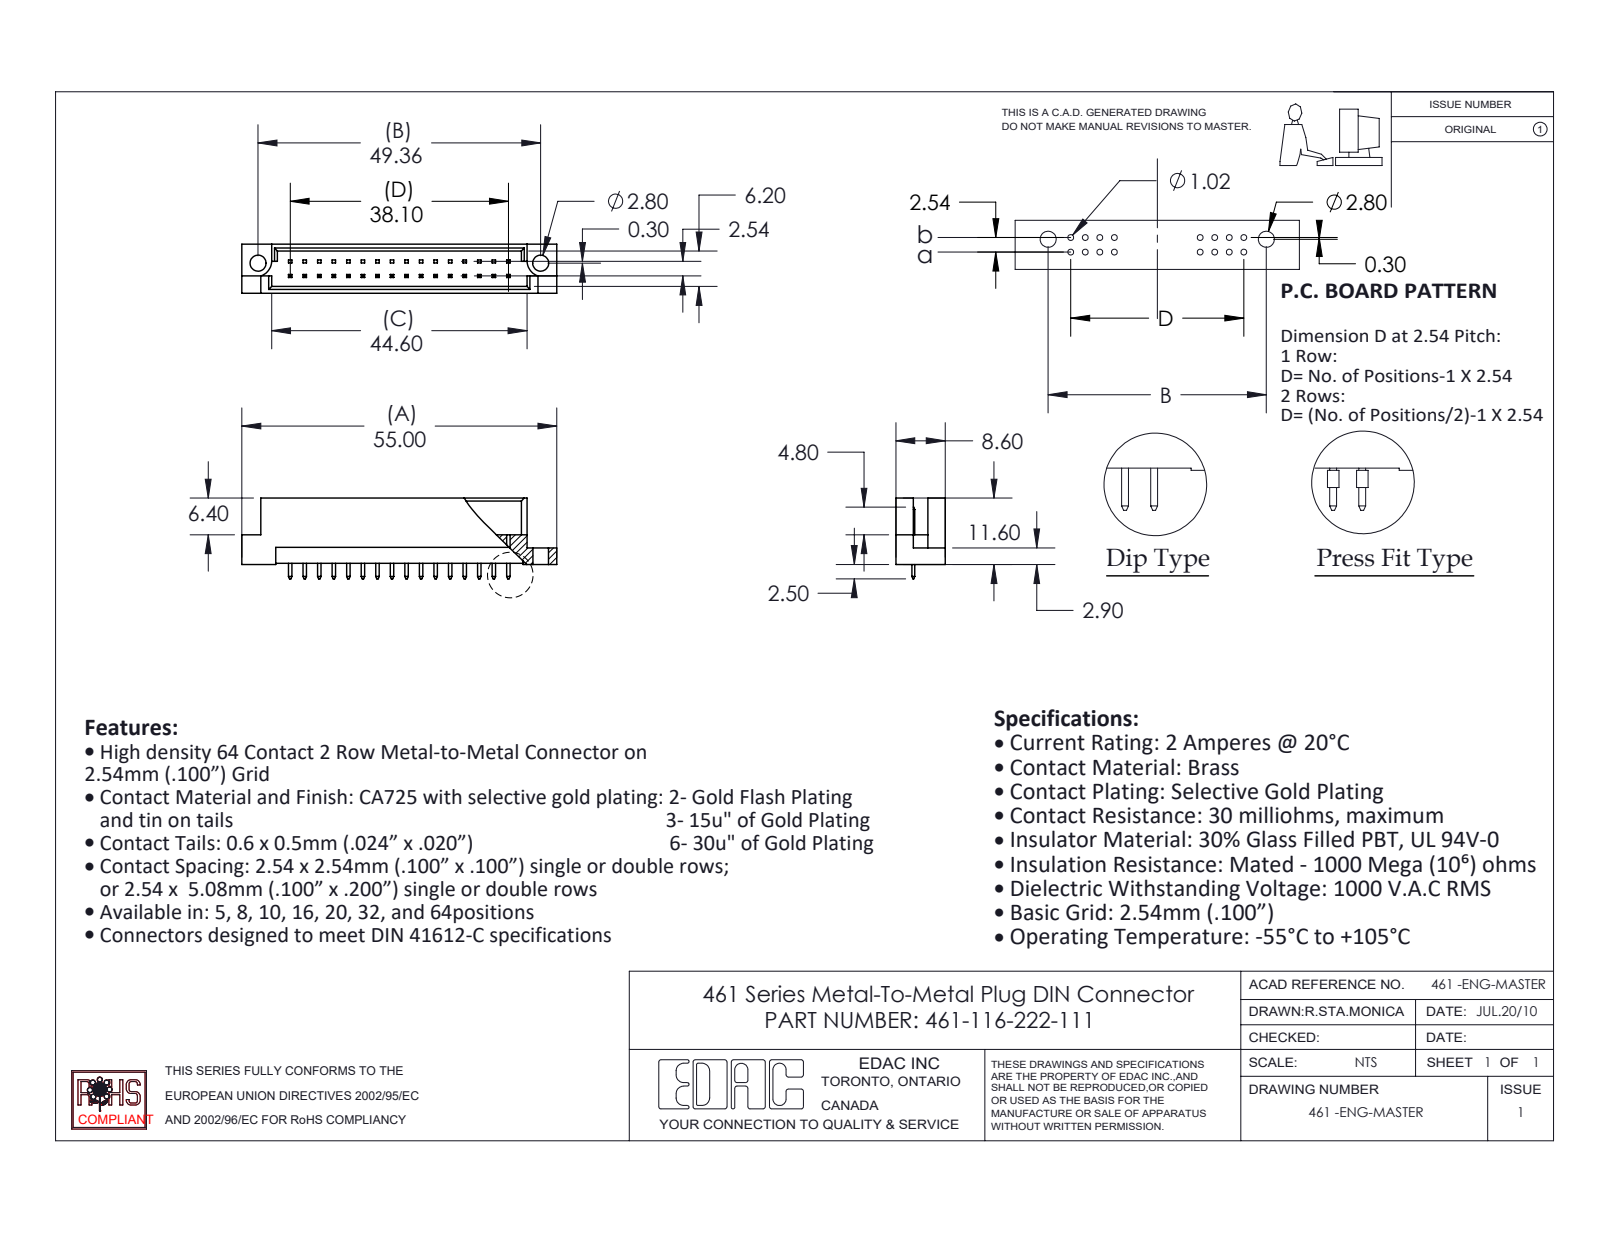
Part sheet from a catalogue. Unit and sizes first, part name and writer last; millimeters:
Units: millimetres
Overall size (bounding box): 55 × 14.1 × 8.6
Round holes (diameter × count): ⌀2.8 ×2
Partial cylindrical surfaces — rounded edges, fillets, slot ends (radius × count): R2.8 ×2
Main face-to-face distances: 1.2, 7.4, 8.6, 6.2, 5, 2.54, 2.78, 5.82, 1.58, 4.62
Hole centre spacings: 49.36
Volume: 2 712 mm³ · Surface area: 3 682 mm²
Bodies: 17 solids, 400 faces (394 planar, 6 cylindrical, 0 other)
Part name (STEP PRODUCT): 461-290_22; 461 Part_32; 461-116-222-111
STEP written by: SolidWorks 2020 (CONFIG_CONTROL_DESIGN)
